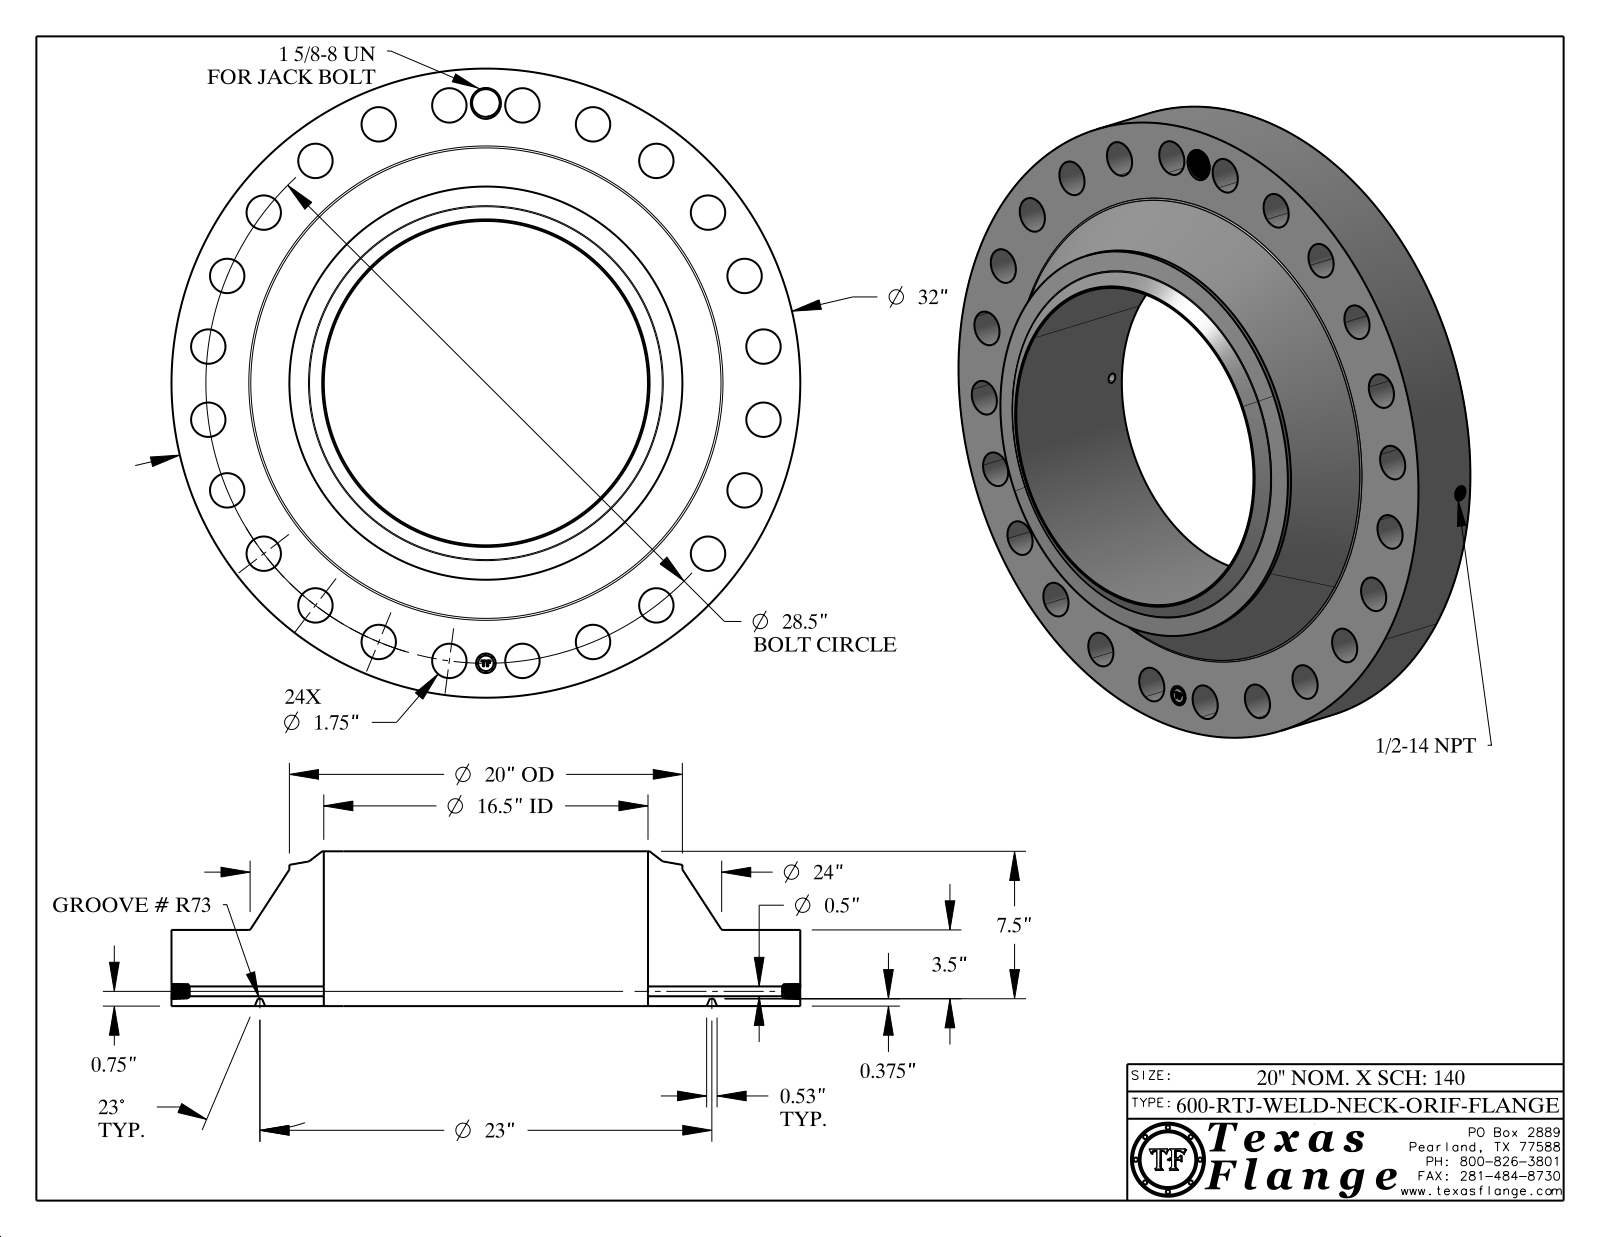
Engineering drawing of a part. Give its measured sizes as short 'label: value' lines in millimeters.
name: 600-RTJ-WELD-NECK
written by: CATIA V5 STEP AP214 (AUTOMOTIVE_DESIGN)
unit: mm
bodies: 1 solid, 908 faces (370 planar, 155 cylindrical, 383 other)
size: 812.8 × 812.8 × 200
volume: 42 700 000 mm³; area: 1 684 000 mm²
holes: 24× ⌀44.5, 1× ⌀12.7, 1× ⌀17.1, 1× ⌀25.4, 1× ⌀35.8, 1× ⌀419.1
bosses: 8× ⌀1.5, 1× ⌀812.8, 1× ⌀508, 1× ⌀20
face distances: 98.4, 9.5, 88.9, 200, 190.5, 101.6, 0.4, 98, 88.5, 102
hole spacings: 362, 440.7, 626.9, 717.7, 277, 94.5, 187.4, 511.9
